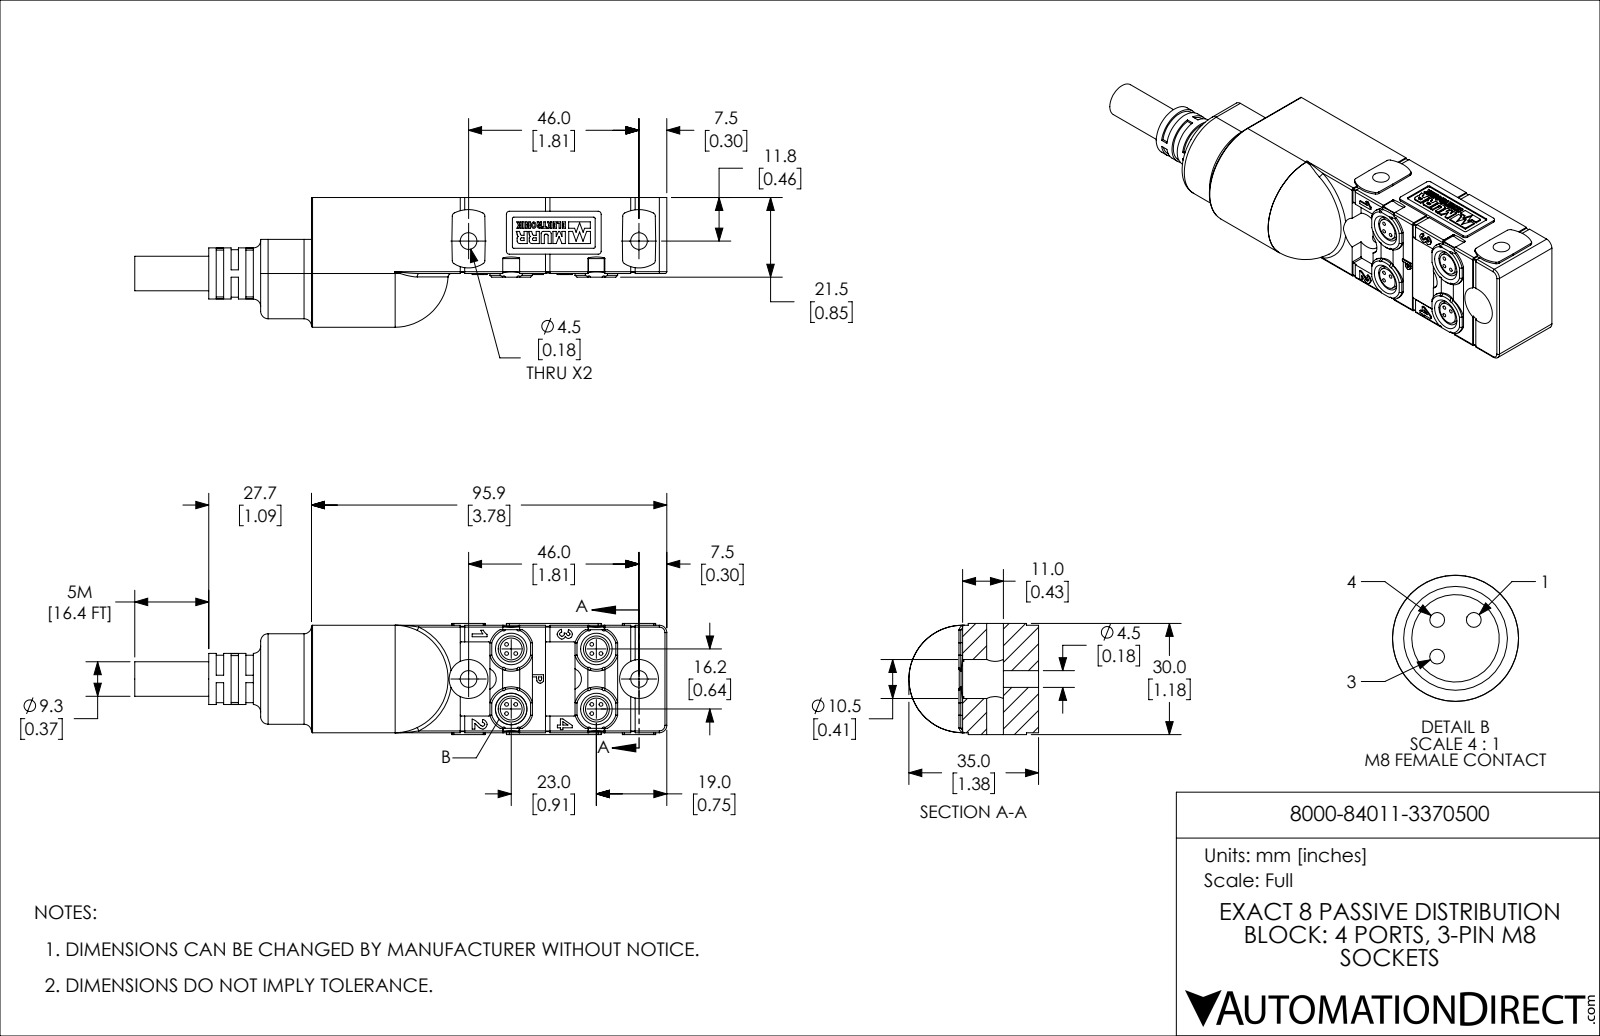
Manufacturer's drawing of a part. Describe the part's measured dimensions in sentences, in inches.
The part is named "8000-84011-3370500". Its 3-D file was written by "SolidWorks 2019 (CONFIG_CONTROL_DESIGN)". It is 1 solid with 971 faces: 581 planar, 285 cylindrical and 105 other. Overall it measures 5.654 by 1.378 by 1.181 inches. Its volume is 4.519 cubic inches and its surface area 25.67 square inches. Round holes: 12 of diameter 0.039, 4 of diameter 0.177, 4 of diameter 0.276, 2 of diameter 0.413. Round bosses or shafts: 4 of diameter 0.232, 1 of diameter 0.543, 1 of diameter 0.504, 1 of diameter 0.449, 1 of diameter 0.366. Partial cylindrical surfaces (rounded edges, fillets, slot ends): 19 of radius 0.02, 12 of radius 0.008, 10 of radius 0.012, 8 of radius 0.039, 6 of radius 0.079, 6 of radius 0.394, 4 of radius 0.012, 4 of radius 0.012. The main face-to-face distances are 1.142, 0.02, 1.161, 0.807, 0.795, 0.433, 0.362, 0.445, 1.181, 3.776. The hole center spacings are 0.069, 0.591, 0.098, 0.638, 0.906, 0.956, 0.138, 0.486.
